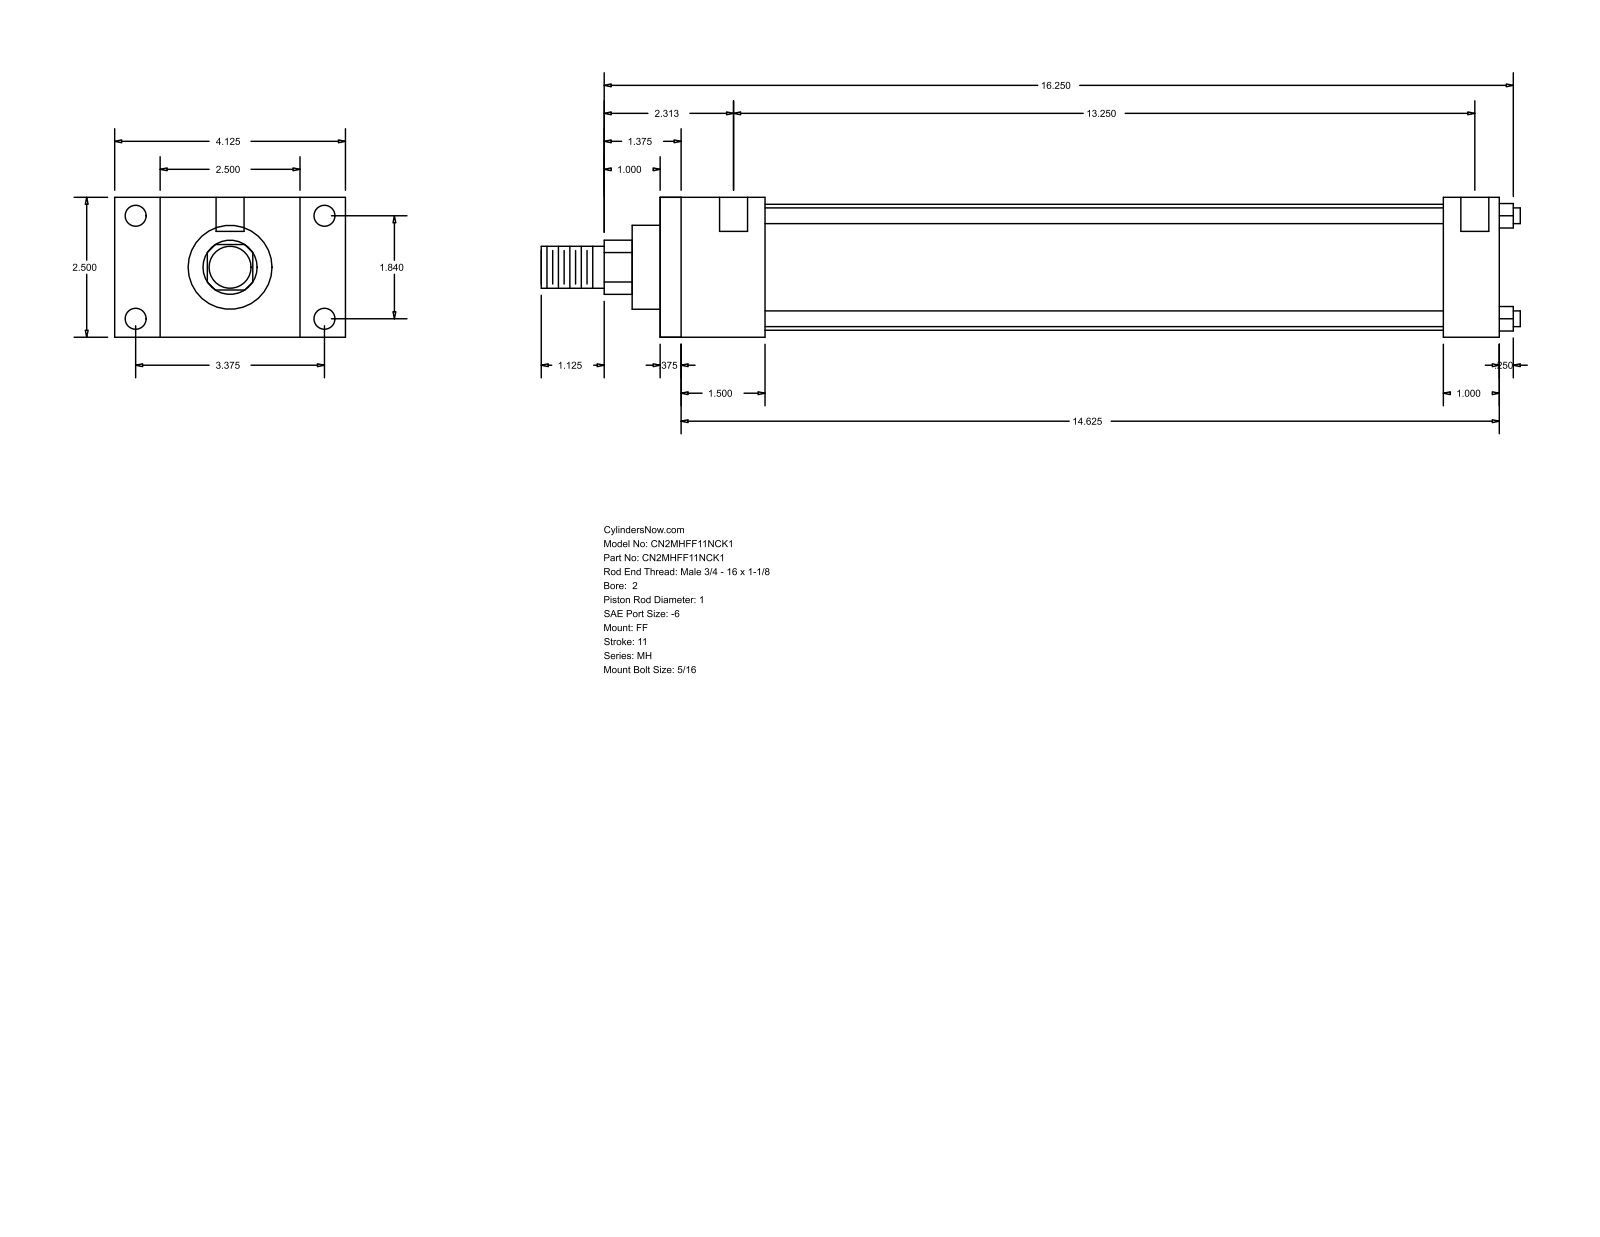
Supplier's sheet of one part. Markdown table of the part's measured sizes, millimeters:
| quantity | value |
| --- | --- |
| part name | MH_FF__0200_1 |
| STEP written by | GSSL Pune (CONFIG_CONTROL_DESIGN) |
| units | millimeters |
| bodies | 0 solids, 92 faces (64 planar, 28 cylindrical, 0 other) |
| overall size | 444.5 × 104.78 × 63.5 |
| round holes (diameter × count) | 5.56 × 4, 9.53 × 4, 12.7 × 2 |
| round bosses / shafts (diameter × count) | 7.14 × 4, 57.15 × 1, 38.1 × 1, 25.4 × 1, 19.05 × 1 |
| partial cylindrical surfaces (radius × count) | 12.29 × 1 |
| main face-to-face distances | 63.5, 381, 9.52, 371.48, 20.64, 25.4, 47.63, 355.6, 38.11, 346.08 |
| hole center spacings | 46.74, 85.72, 97.63, 344.48, 3.17, 4.76, 336.55, 339.72 |
